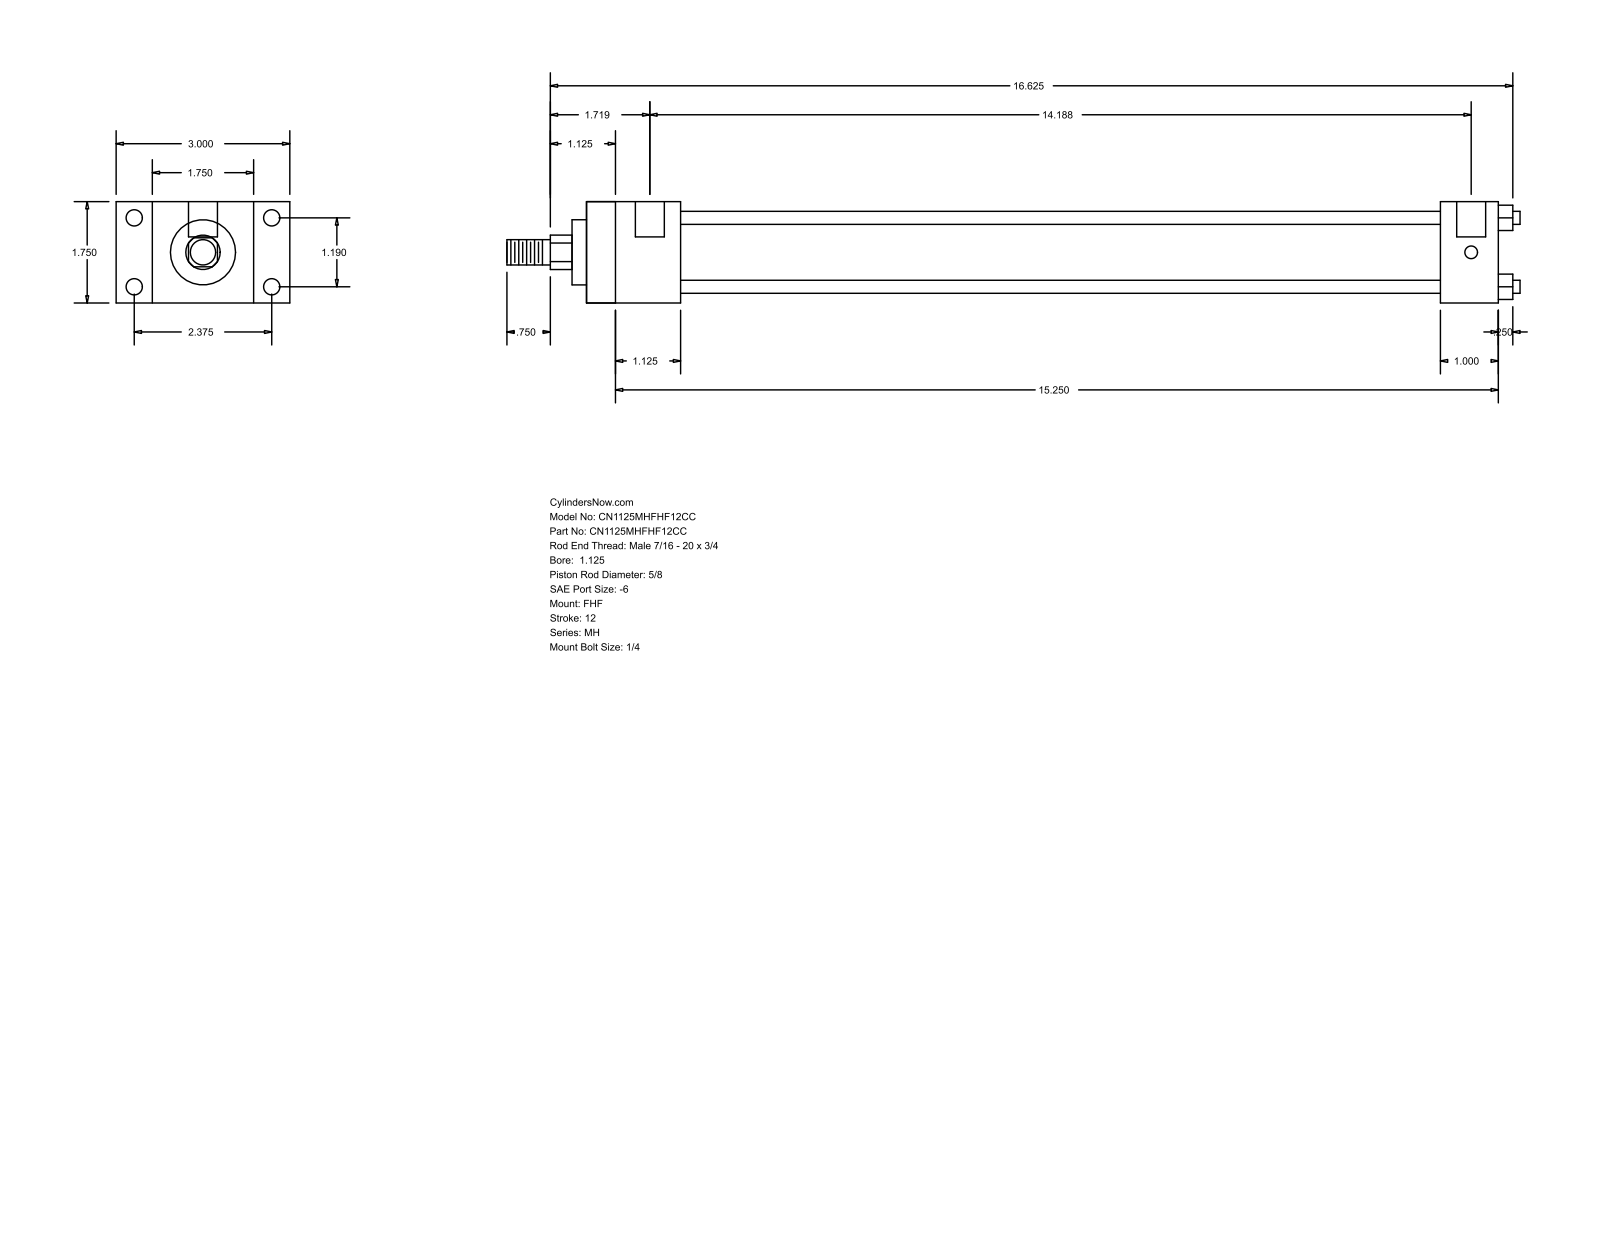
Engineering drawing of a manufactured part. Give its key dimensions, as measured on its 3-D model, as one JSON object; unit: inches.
{"part_name": "MH_FHF__0112_0.625", "step_written_by": "GSSL Pune (CONFIG_CONTROL_DESIGN)", "units": "inches", "bodies": {"solids": 0, "faces": 88, "planar": 60, "cylindrical": 28, "other": 0}, "overall_size": [17.5, 3, 1.75], "round_holes": [[0.219, 4], [0.281, 4], [0.5, 2]], "round_bosses_or_shafts": [[0.225, 4], [1.375, 1], [1.125, 1], [0.625, 1], [0.437, 1]], "partial_cylinders_radius": [[0.297, 1]], "face_to_face_distances": [1.75, 0.625, 2.375, 1.625, 3, 15.75, 14.125, 14.75, 13.125, 1], "hole_center_spacings": [1.19, 2.375, 2.656, 14.063, 0.125, 14.187]}
